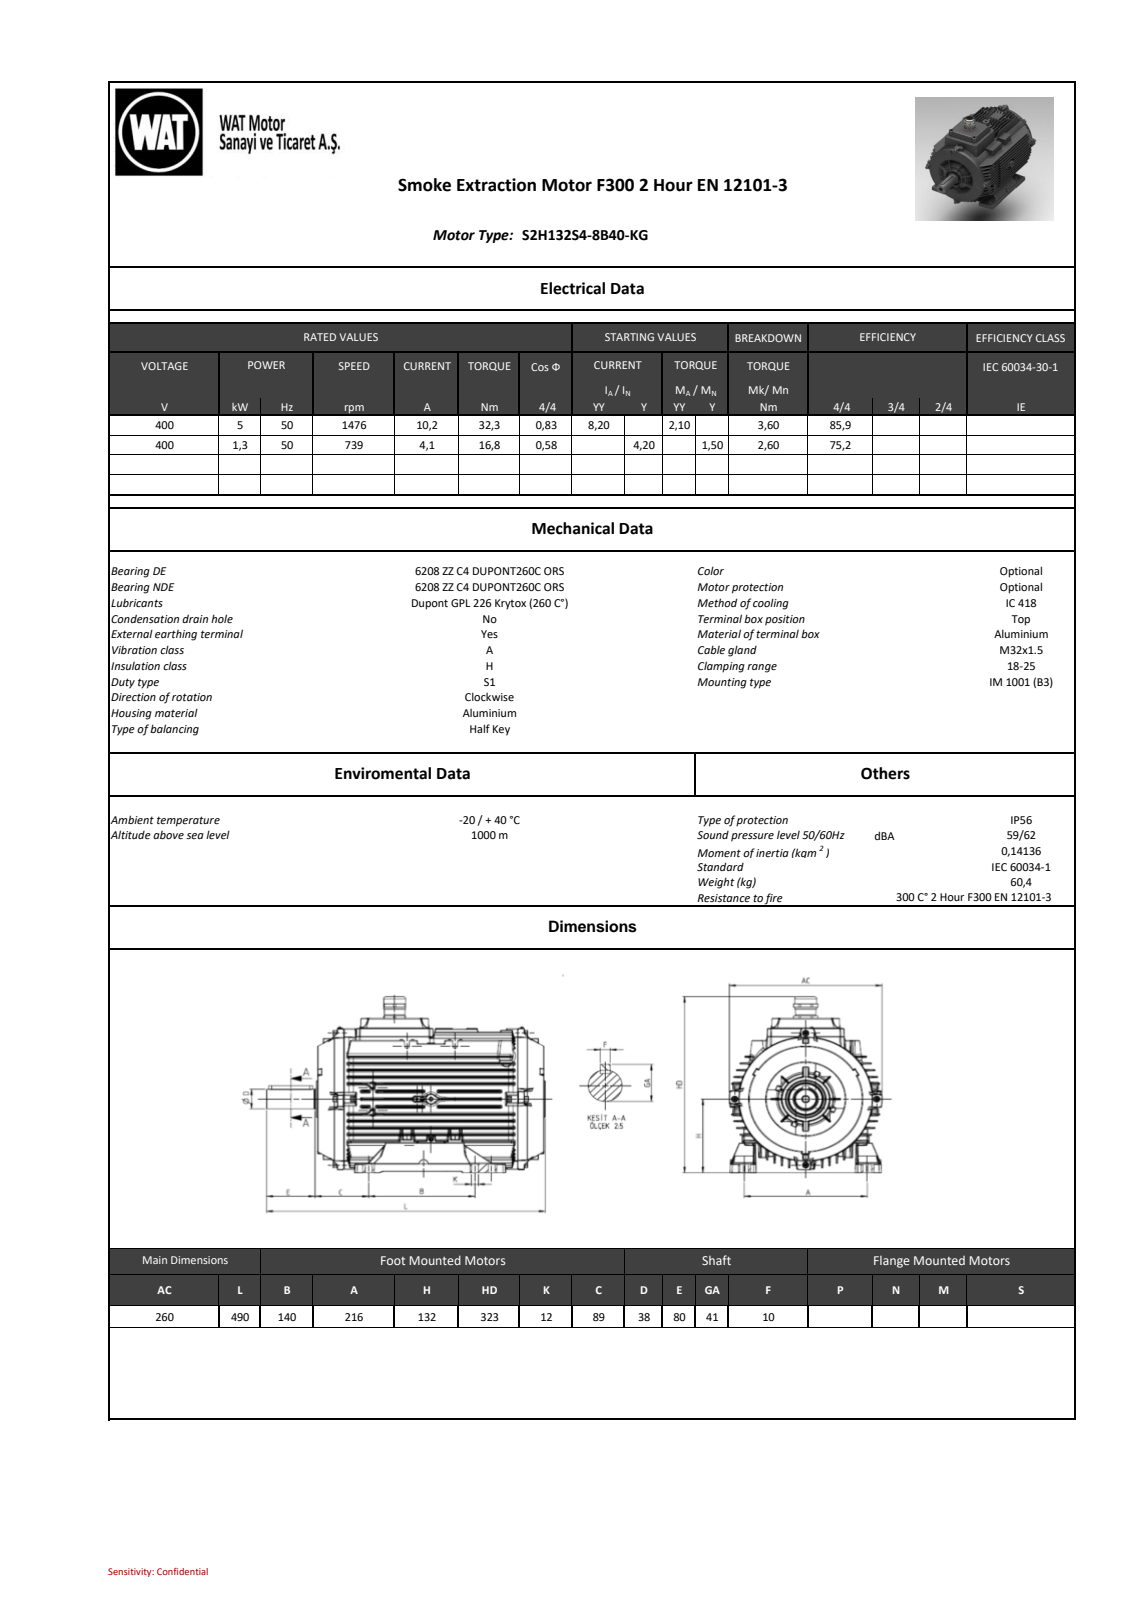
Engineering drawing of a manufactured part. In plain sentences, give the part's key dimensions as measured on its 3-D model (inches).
The part is named "260314206C66eeft". Its 3-D file was written by "SIEMENS PLM Software NX 11.0 (AP203_CONFIGURATION_CONTROLLED_3D_DESIGN_OF_MECHANICAL_PARTS_AND_ASSEMBLIES_MIM_LF)". It is 0 solids with 8089 faces: 1705 planar, 2802 cylindrical and 3582 other. Overall it measures 19.272 by 12.724 by 10.236 inches. Round holes: 3 of diameter 0.165, 2 of diameter 0.268, 2 of diameter 0.315, 1 of diameter 0.413, 1 of diameter 0.709, 1 of diameter 1.732, 1 of diameter 2.299, 1 of diameter 2.307. Round bosses or shafts: 4 of diameter 0.583, 4 of diameter 0.512, 4 of diameter 0.394, 1 of diameter 9.075, 1 of diameter 1.575, 1 of diameter 1.496, 1 of diameter 1.472, 1 of diameter 1.165. Partial cylindrical surfaces (rounded edges, fillets, slot ends): 1047 of radius 0.031, 696 of radius 0.039, 111 of radius 0.059, 70 of radius 0.02, 68 of radius 0.079, 22 of radius 0.118, 12 of radius 0.197, 10 of radius 0.004. The main face-to-face distances are 0.41, 0.416, 0.82, 0.405, 4.944, 3.309, 4.535, 4.13, 3.719, 0.409. The hole center spacings are 1.26, 10.295.
